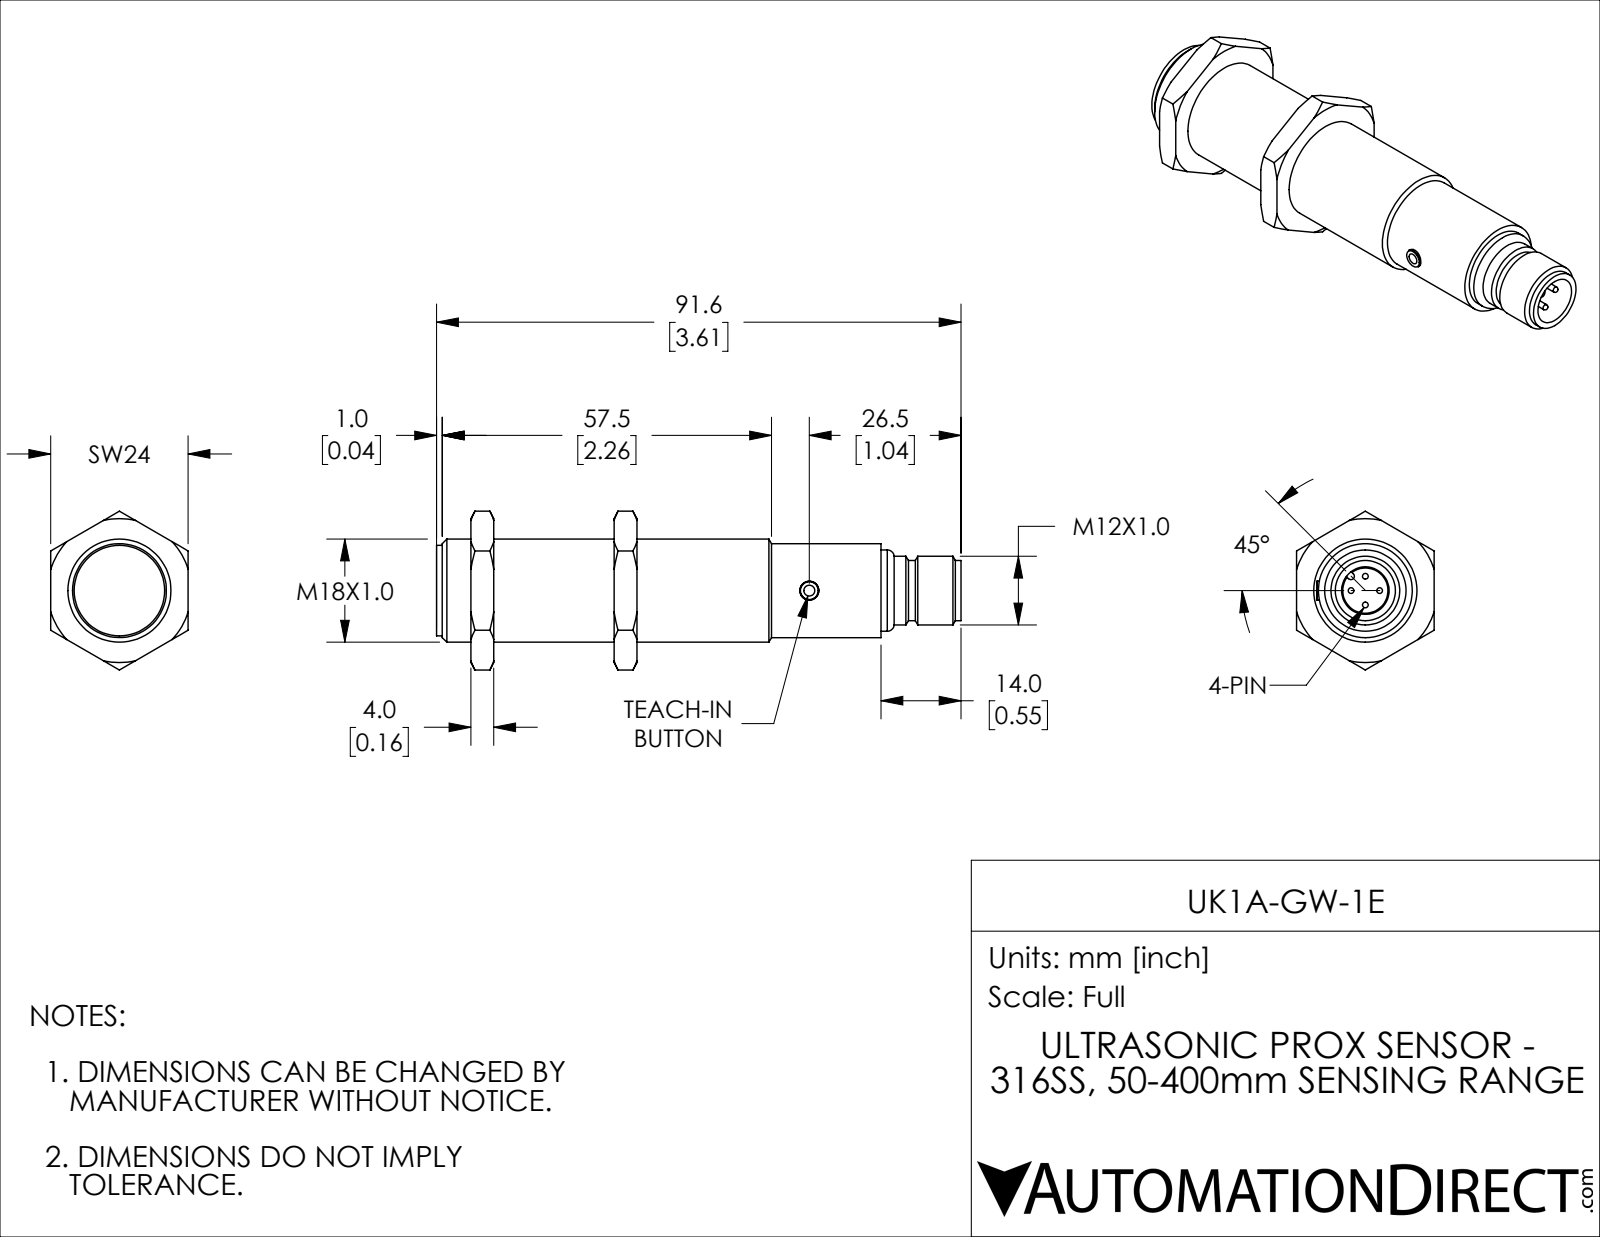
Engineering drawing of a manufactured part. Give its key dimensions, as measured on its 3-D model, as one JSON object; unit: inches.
{"part_name": "UK1A-GW-1E", "step_written_by": "SolidWorks 2018 (AUTOMOTIVE_DESIGN)", "units": "inches", "bodies": {"solids": 4, "faces": 113, "planar": 27, "cylindrical": 35, "other": 51}, "overall_size": [3.606, 1.091, 0.945], "volume_in3": 1.338, "surface_area_in2": 11.97, "round_holes": [[0.13, 1], [0.327, 1], [0.709, 1]], "round_bosses_or_shafts": [[0.039, 4], [0.646, 1], [0.622, 1], [0.559, 1], [0.472, 1], [0.413, 1]], "partial_cylinders_radius": [[0.024, 1]], "face_to_face_distances": [0.984, 0.157, 0.945, 1.142, 0.827, 0.236, 0.394, 1.22, 1.378, 3.055]}
